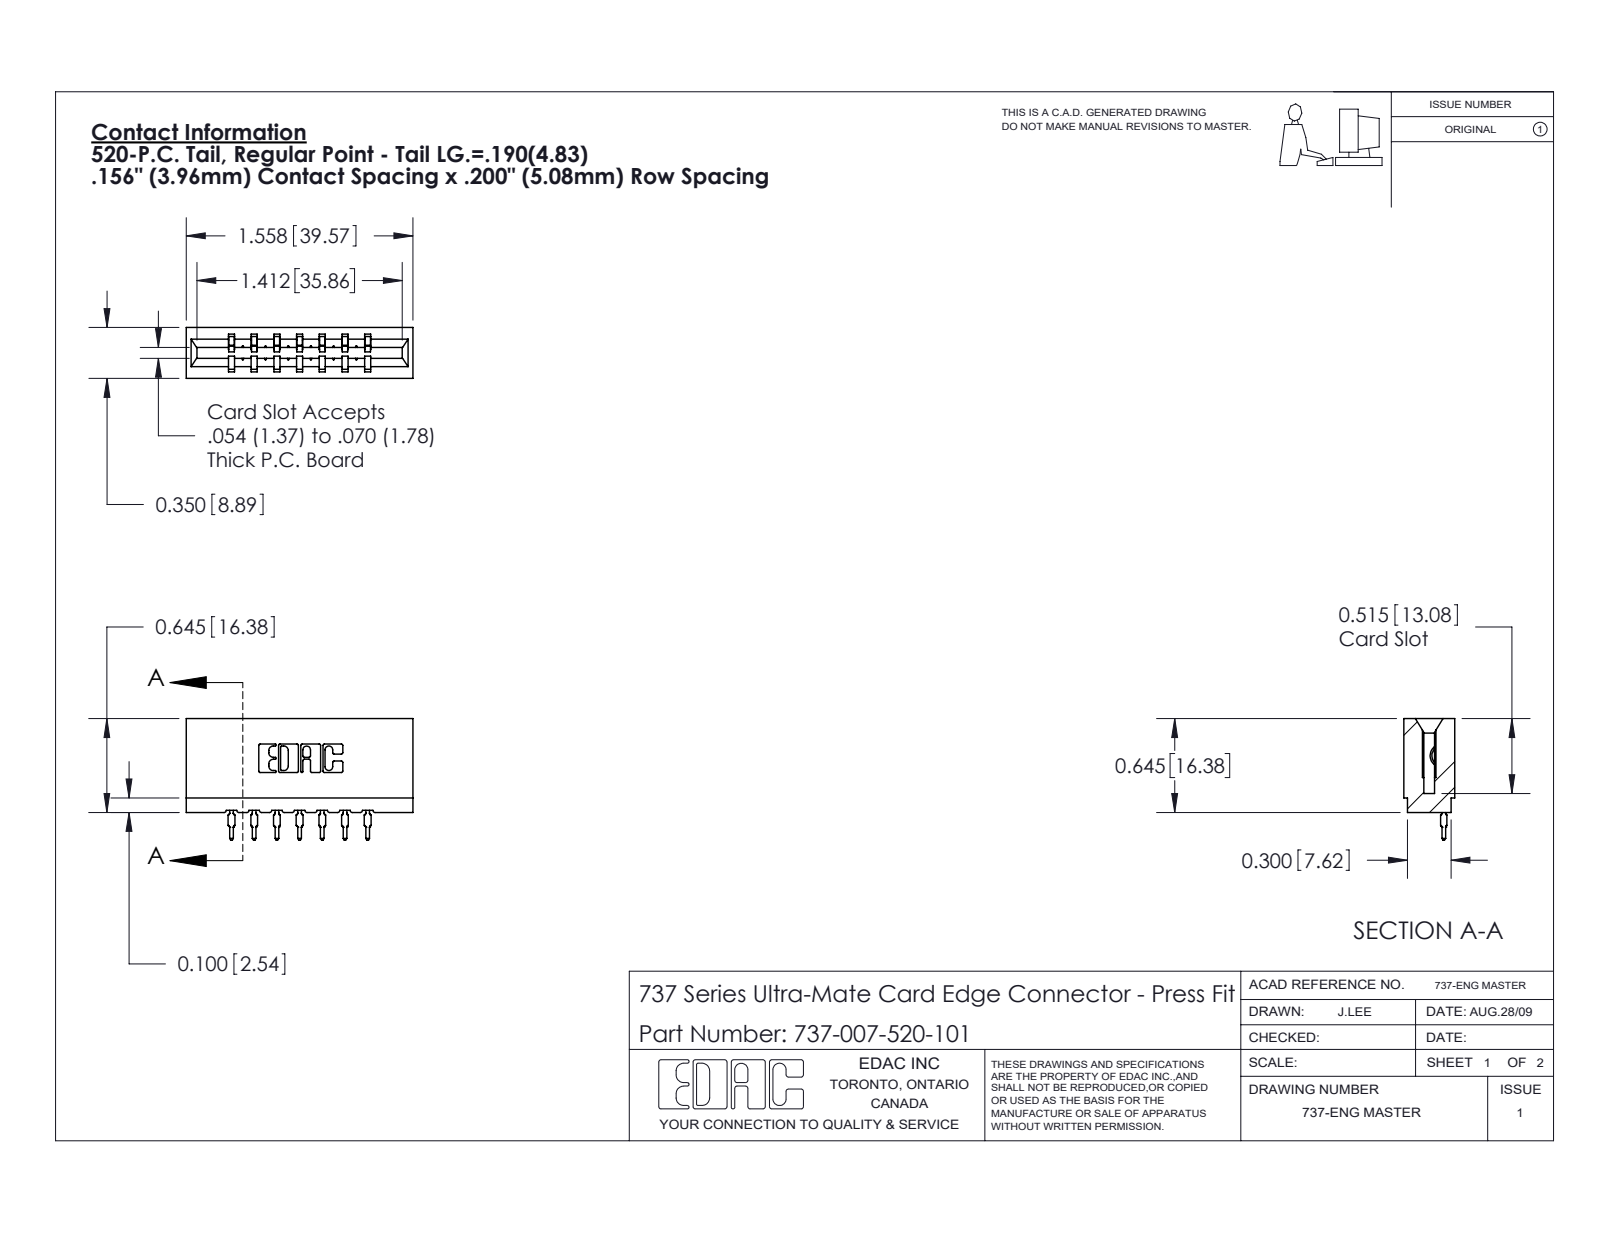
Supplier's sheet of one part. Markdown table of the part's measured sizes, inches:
| quantity | value |
| --- | --- |
| part name | 745-292-001_520; 737-007-520-101; 737 Part_Insulator Option - 01 |
| STEP written by | SolidWorks 2020 (CONFIG_CONTROL_DESIGN) |
| units | inches |
| bodies | 8 solids, 885 faces (530 planar, 173 cylindrical, 182 other) |
| overall size | 1.558 × 0.836 × 0.35 |
| volume | 0.248 in³ |
| surface area | 7.375 in² |
| partial cylindrical surfaces (radius × count) | 0.01 × 22, 0.015 × 14, 0.021 × 14, 0.007 × 6, 0.031 × 6, 0.005 × 4, 0.011 × 4, 0.026 × 3 |
| main face-to-face distances | 0.156, 0.138, 0.212, 0.35, 0.312, 0.354, 0.198, 0.624, 0.468, 0.074 |
